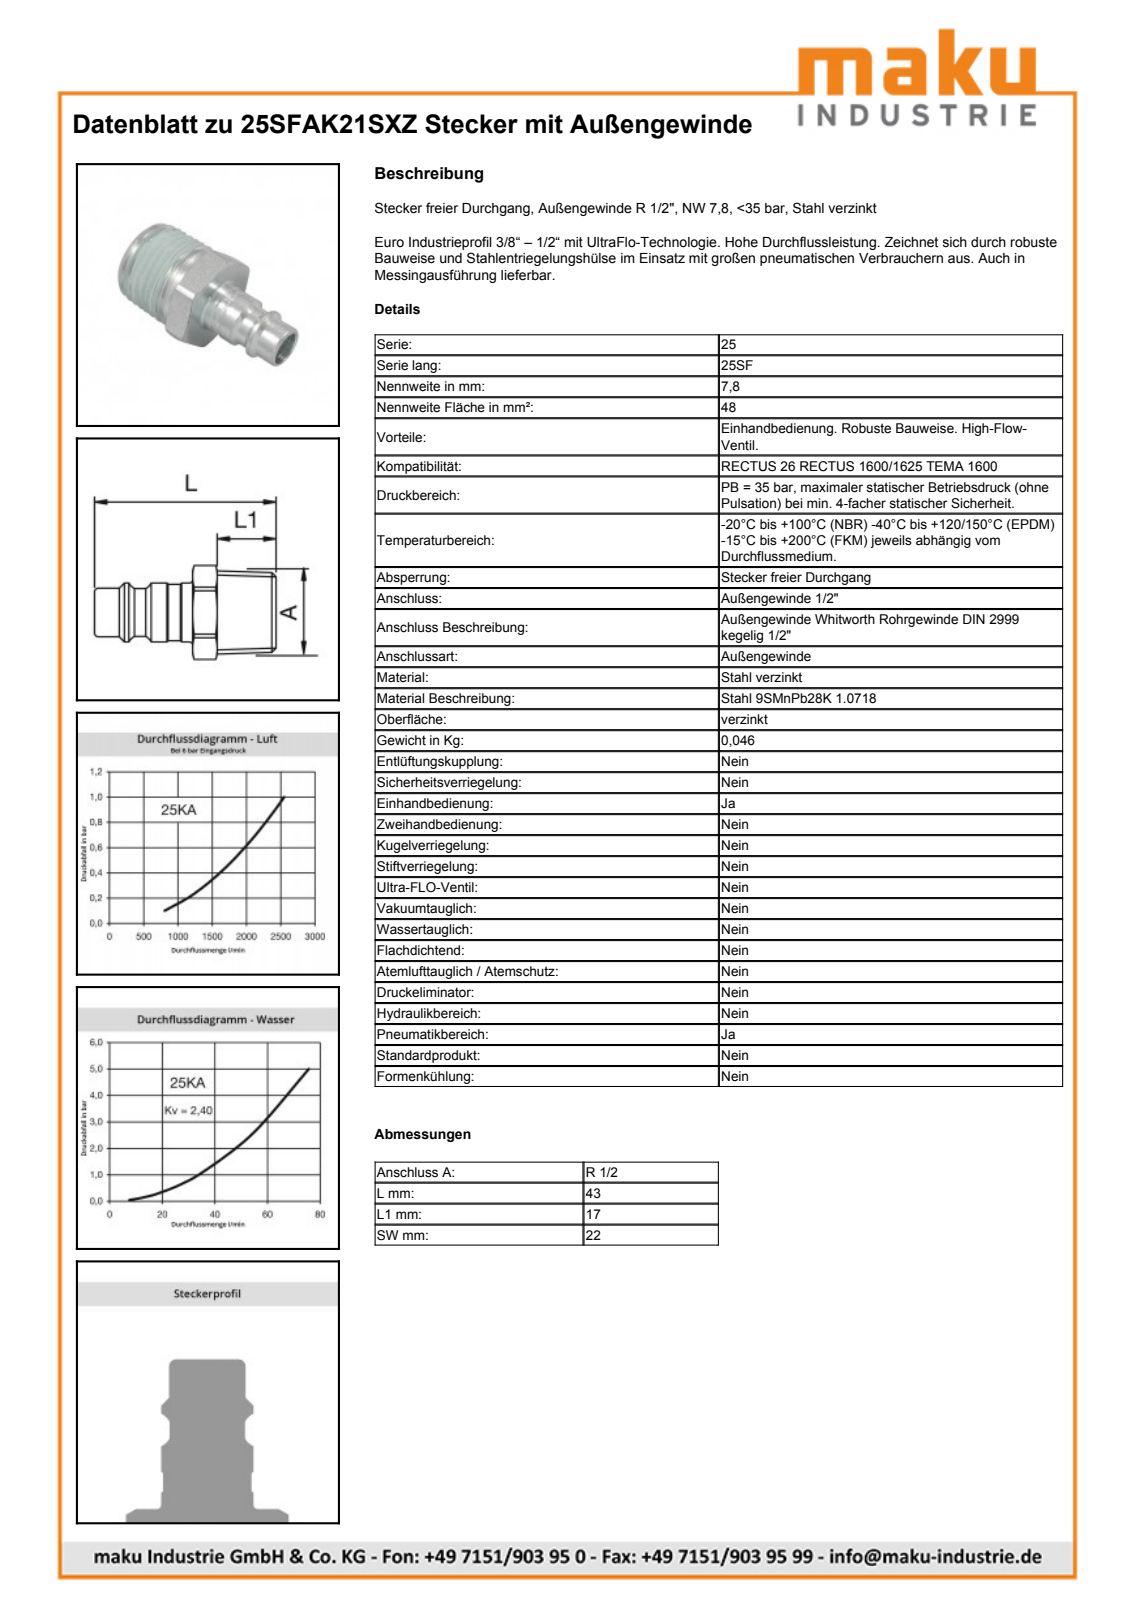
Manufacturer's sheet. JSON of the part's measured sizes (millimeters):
{"part_name": "D106828", "step_written_by": "Autodesk Inventor 2013 (AUTOMOTIVE_DESIGN)", "units": "millimeters", "bodies": {"solids": 1, "faces": 42, "planar": 10, "cylindrical": 12, "other": 20}, "overall_size": [43, 24.8, 22], "volume_mm3": 6466, "surface_area_mm2": 4235, "round_holes": [[7.85, 1], [13, 1]], "round_bosses_or_shafts": [[12, 1], [9.9, 1], [9.75, 1]], "partial_cylinders_radius": [[12.4, 1]], "face_to_face_distances": [22, 23, 6, 17, 20, 26, 43]}
